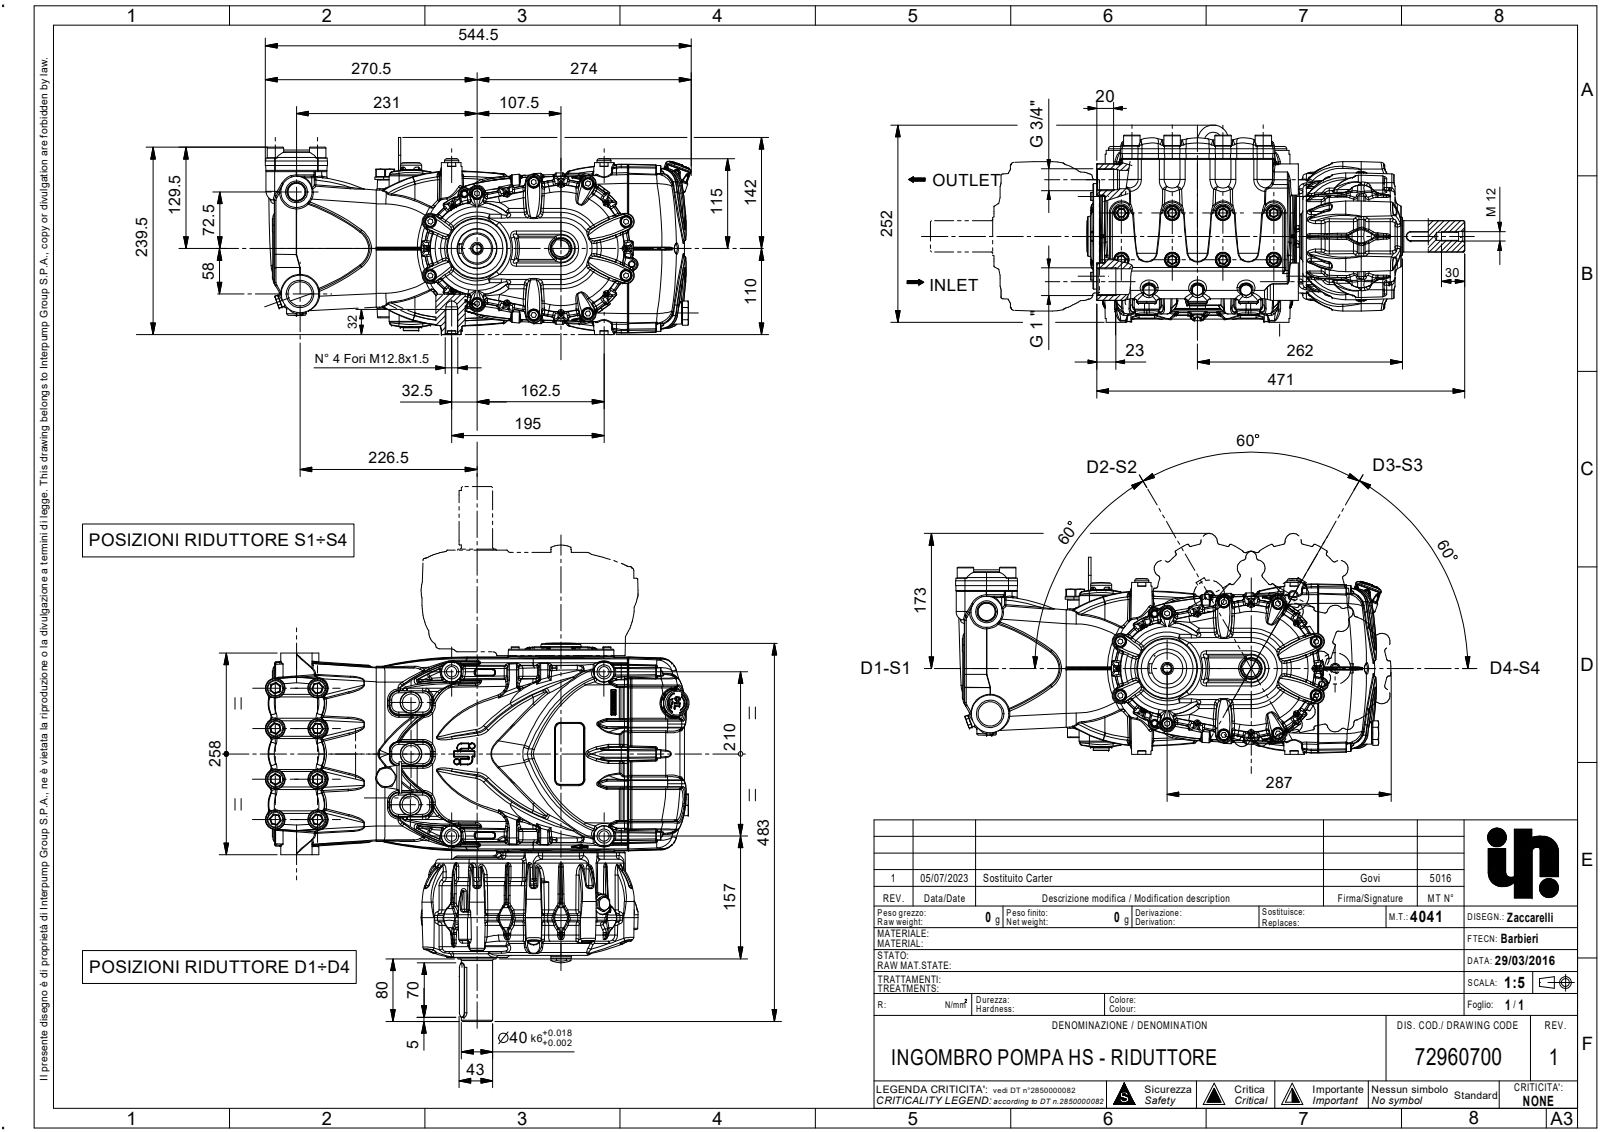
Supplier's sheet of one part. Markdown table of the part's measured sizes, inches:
| quantity | value |
| --- | --- |
| STEP written by | THINKDESIGN (CONFIG_CONTROL_DESIGN) |
| units | inches |
| bodies | 77 solids, 12577 faces (2072 planar, 2872 cylindrical, 7633 other) |
| overall size | 21.442 × 19.044 × 9.93 |
| volume | 1 646 in³ |
| surface area | 2 206 in² |
| round holes (diameter × count) | 0.315 × 8, 0.748 × 8, 0.236 × 4, 0.202 × 3, 0.256 × 3, 0.354 × 2, 0.413 × 1, 0.48 × 1, 0.531 × 1, 0.65 × 1, 0.728 × 1, 0.825 × 1 |
| round bosses / shafts (diameter × count) | 0.394 × 18, 0.512 × 16, 0.315 × 16, 0.709 × 14, 0.236 × 14, 0.551 × 12, 0.827 × 8, 0.472 × 8 |
| partial cylindrical surfaces (radius × count) | 0.004 × 458, 0.02 × 397, 0.008 × 182, 0.079 × 177, 0.059 × 159, 0.118 × 154, 0.039 × 115, 0.138 × 72 |
| main face-to-face distances | 12.657, 0.276, 12.382, 9.244, 0.439, 9.683, 0.02, 3.307, 3.327, 9.843 |
| hole center spacings | 2.559, 3.483, 2.362, 5.118, 5.637, 7.677, 0.394, 2.313 |
